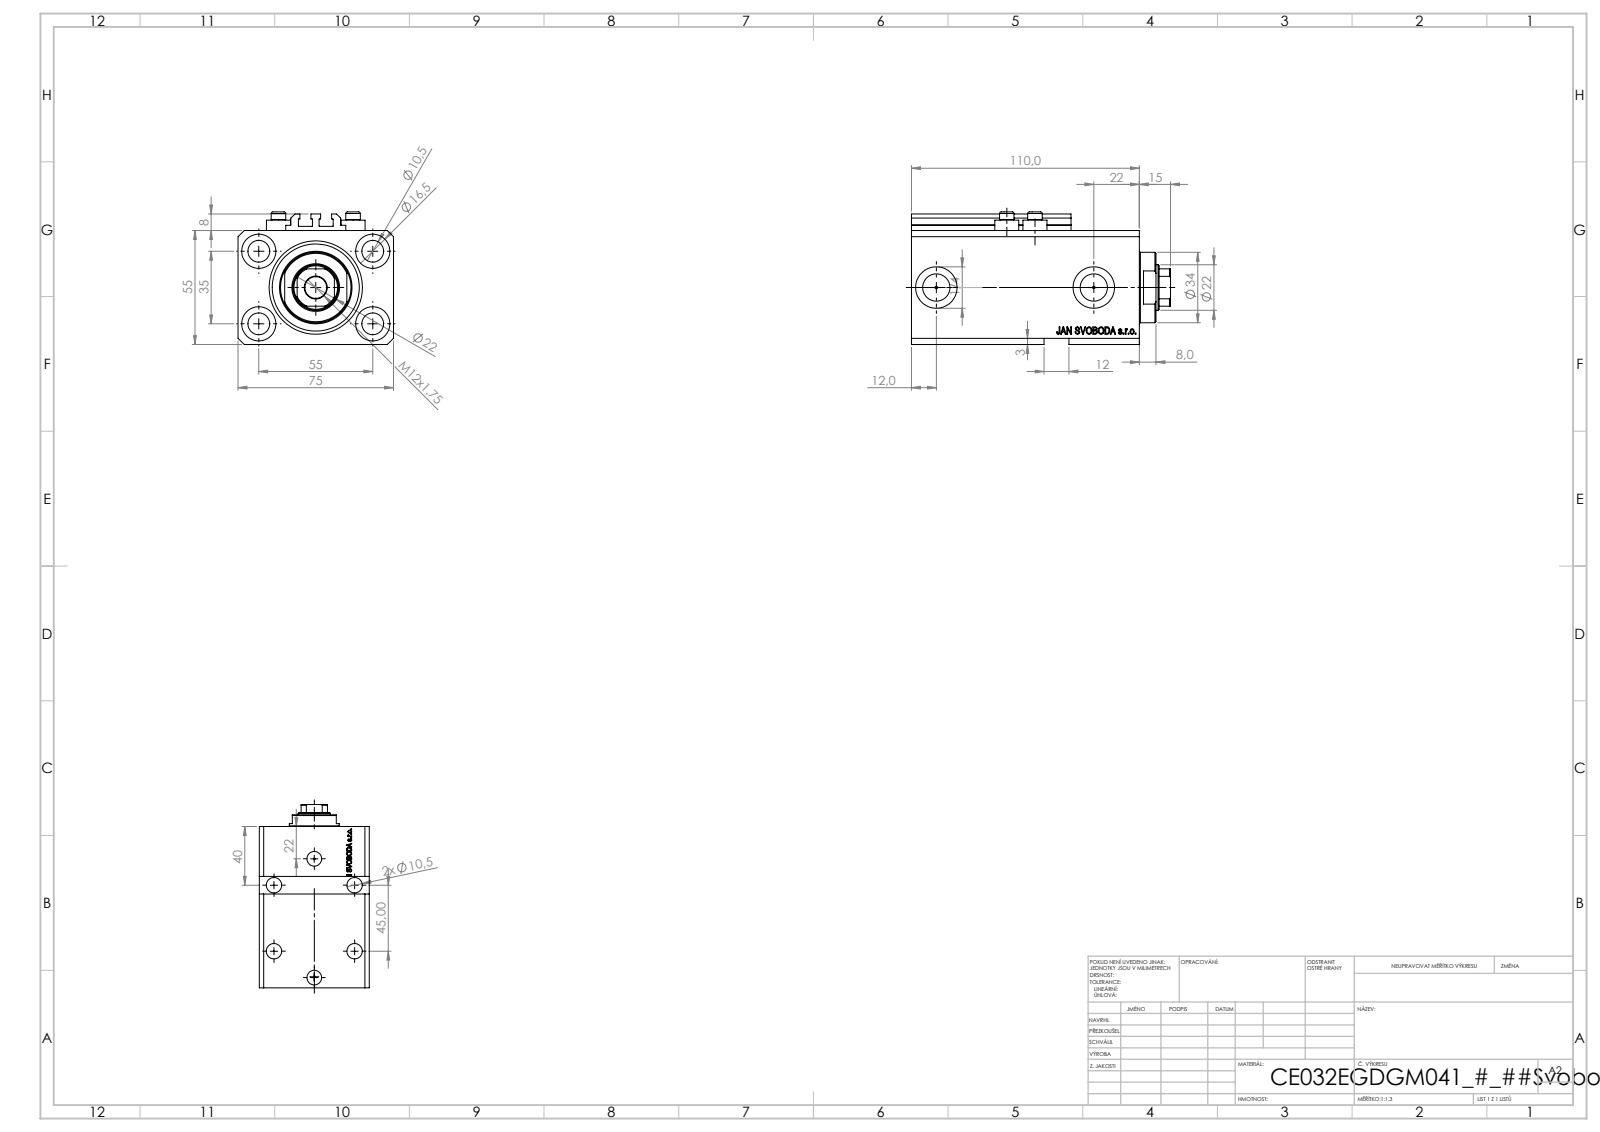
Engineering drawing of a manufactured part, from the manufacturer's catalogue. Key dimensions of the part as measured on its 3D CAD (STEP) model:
Part name (STEP PRODUCT): V250CE_E_Body; ALLEN BOLT V250CE; V250CE_C_VCP; V250CE_VC_E
STEP written by: SolidWorks 2019 (CONFIG_CONTROL_DESIGN)
Units: millimetres
Bodies: 8 solids, 1100 faces (518 planar, 158 cylindrical, 424 other)
Overall size (bounding box): 125 × 75 × 64
Volume: 377 718 mm³ · Surface area: 96 791 mm²
Round holes (diameter × count): ⌀10.5 ×9, ⌀1.25 ×4, ⌀4 ×4, ⌀16.5 ×4, ⌀10 ×2, ⌀13.16 ×2, ⌀20 ×2, ⌀22 ×1, ⌀32 ×1, ⌀45 ×1
Round bosses / shafts (diameter × count): ⌀11.6 ×4, ⌀7 ×4, ⌀34 ×1
Partial cylindrical surfaces — rounded edges, fillets, slot ends (radius × count): R0.2 ×10, R10.5 ×1
Main face-to-face distances: 55, 75, 15, 110, 95, 9.9, 3, 85.1, 100.1, 57
Hole centre spacings: 32.6, 32.87, 55, 68.74, 13.6, 14.09, 23.05, 25.81
